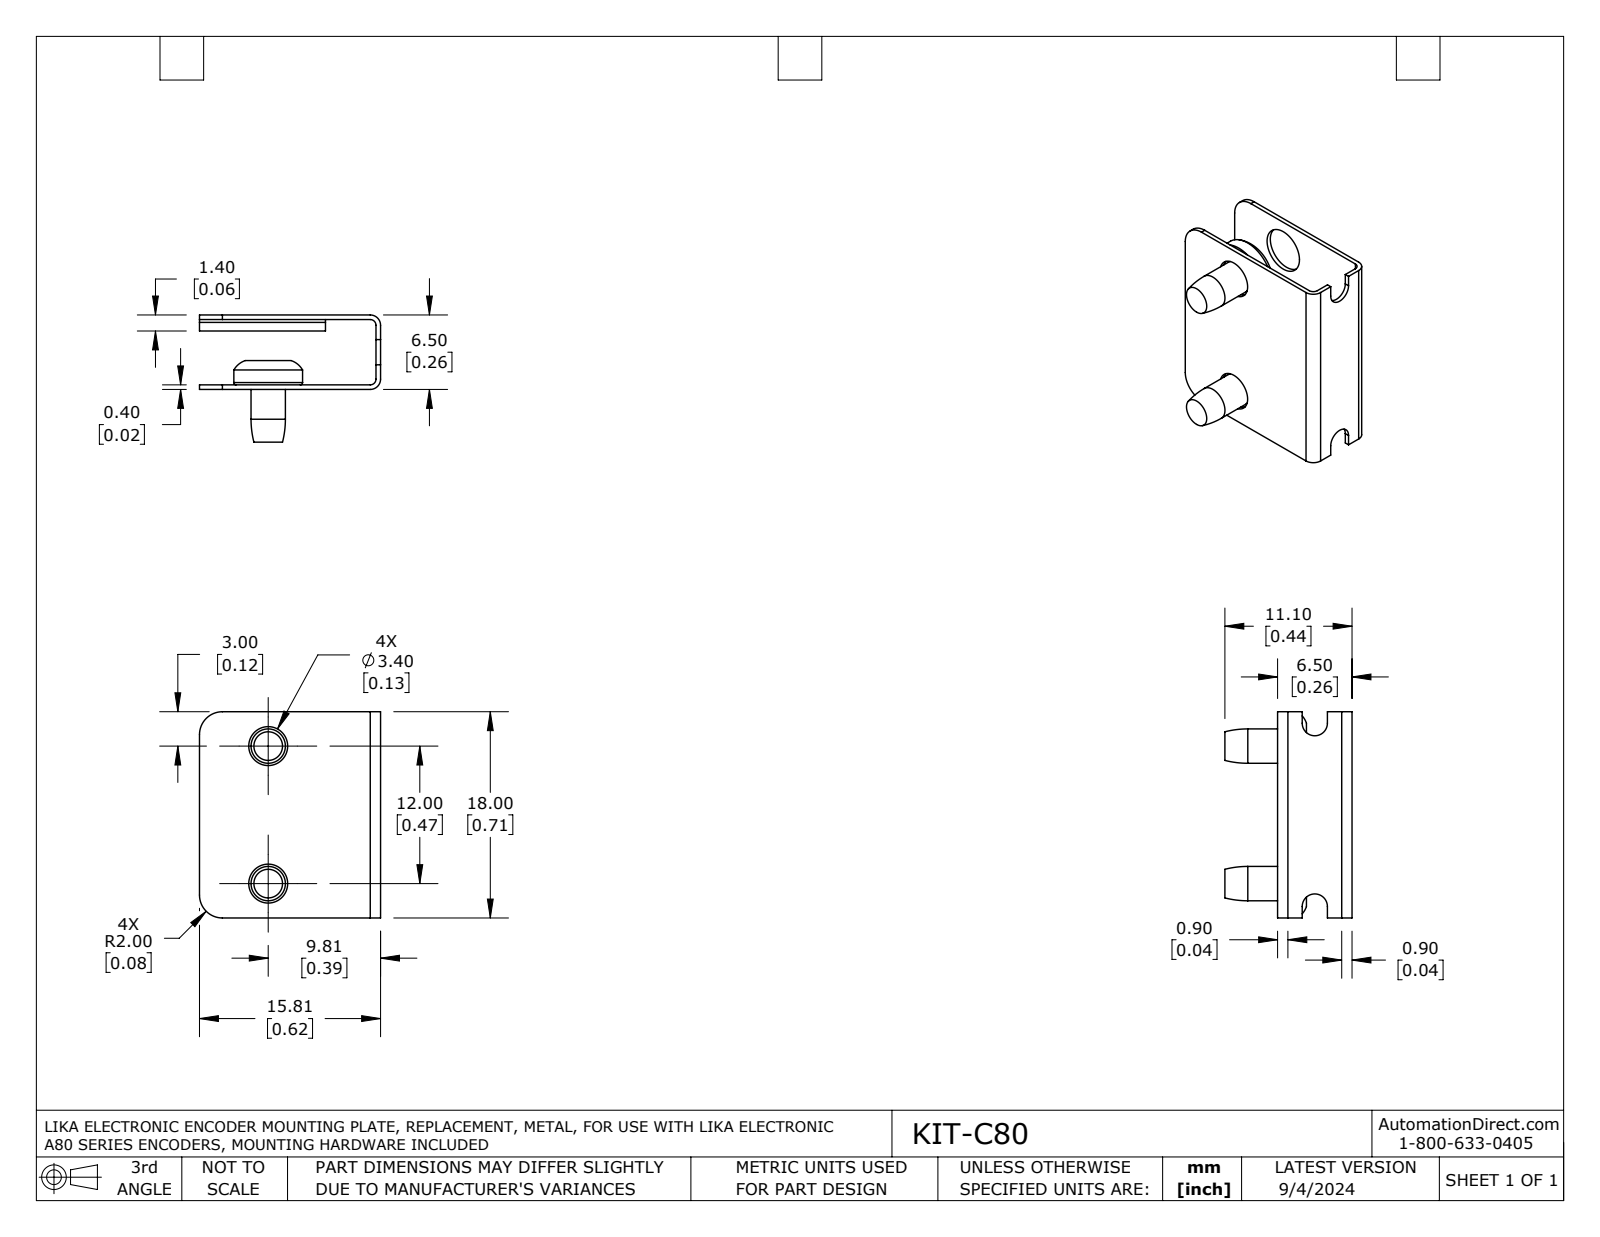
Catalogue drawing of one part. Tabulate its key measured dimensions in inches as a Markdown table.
| quantity | value |
| --- | --- |
| part name | KIT-C80 |
| STEP written by | SolidWorks 2021 (AUTOMOTIVE_DESIGN) |
| units | inches |
| bodies | 3 solids, 124 faces (36 planar, 72 cylindrical, 16 other) |
| overall size | 0.709 × 0.622 × 0.437 |
| volume | 0.024 in³ |
| surface area | 2.364 in² |
| round holes (diameter × count) | 0.134 × 2, 0.157 × 2 |
| round bosses / shafts (diameter × count) | 0.236 × 2, 0.118 × 2 |
| partial cylindrical surfaces (radius × count) | 0.01 × 14, 0.017 × 12, 0.02 × 2, 0.026 × 2, 0.035 × 2, 0.043 × 2, 0.079 × 2 |
| main face-to-face distances | 0.016, 0.24, 0.256, 0.224, 0.28, 0.295, 0.413, 0.429, 0.134, 0.039 |
| hole center spacings | 0.472 |
